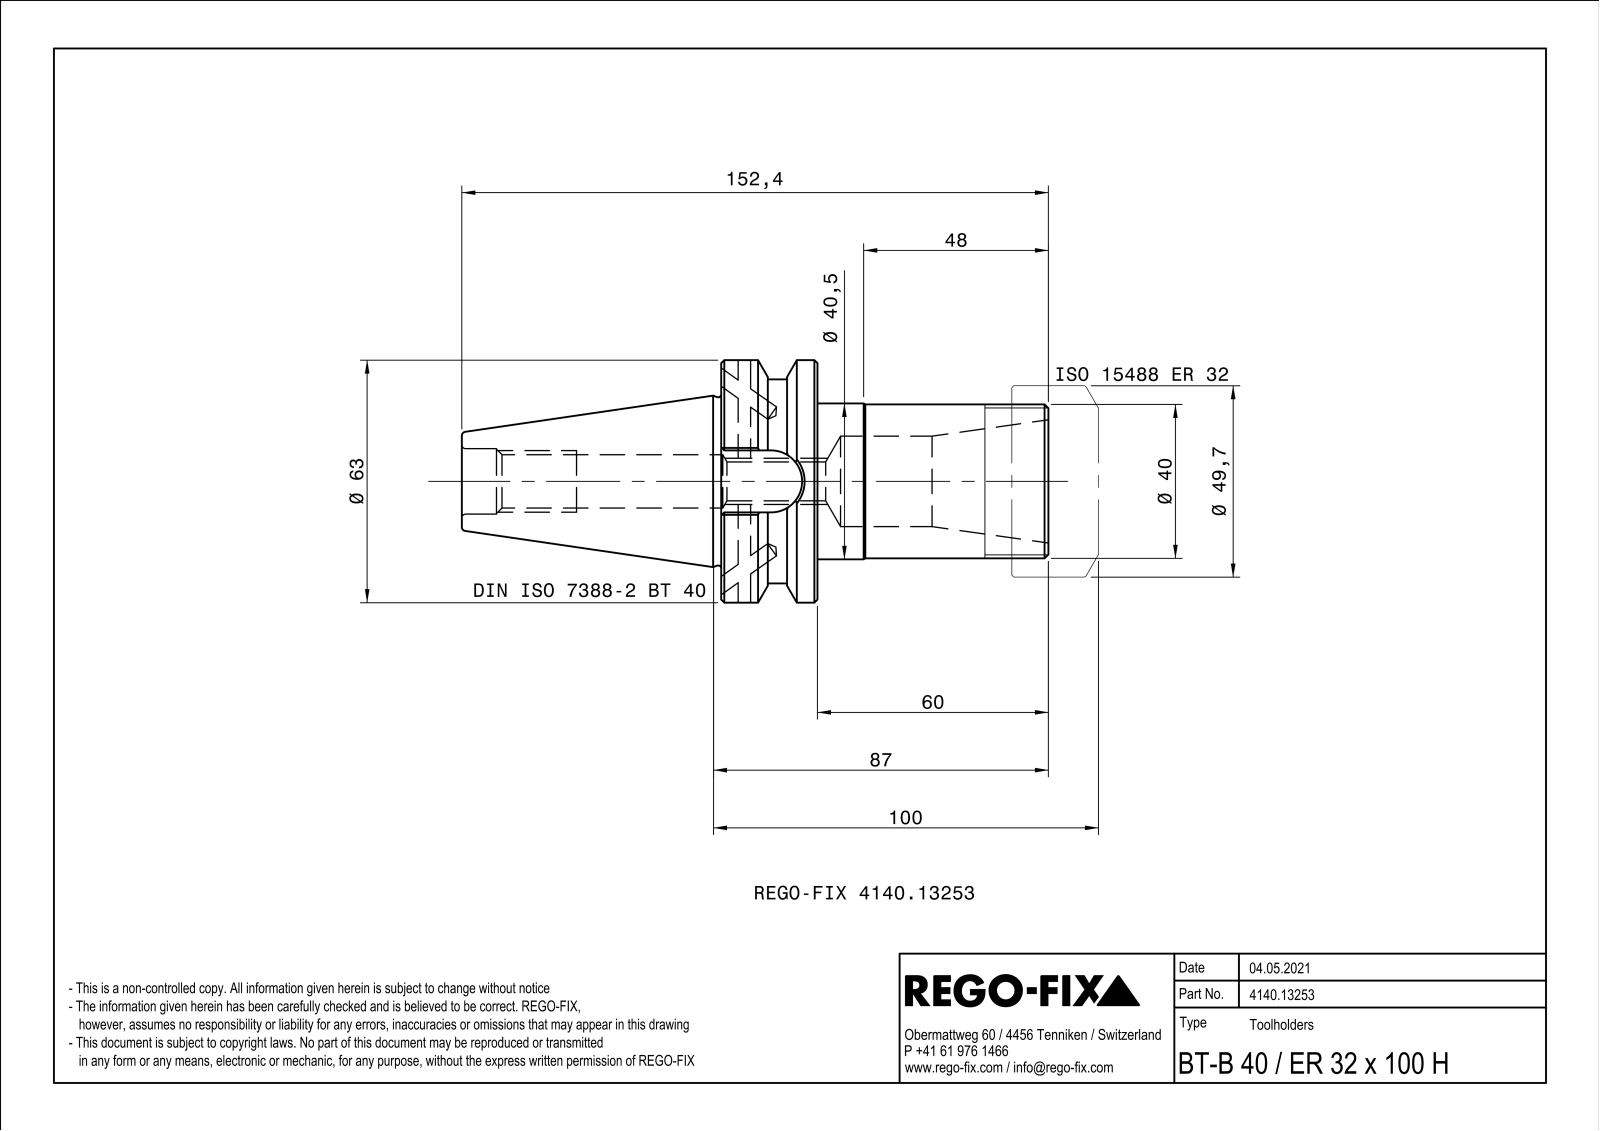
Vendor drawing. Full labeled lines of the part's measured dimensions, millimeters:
Part name (STEP PRODUCT): NOCUT
STEP written by: SIEMENS PLM Software Solid Edge ST10 (AUTOMOTIVE_DESIGN)
Units: millimetres
Bodies: 1 solid, 104 faces (36 planar, 29 cylindrical, 39 other)
Overall size (bounding box): 152.4 × 63 × 63
Volume: 166 506 mm³ · Surface area: 34 576 mm²
Round holes (diameter × count): ⌀3.24 ×2, ⌀3.9 ×2, ⌀10.11 ×1, ⌀13.83 ×1, ⌀13.84 ×1, ⌀17 ×1, ⌀23.5 ×1
Round bosses / shafts (diameter × count): ⌀63 ×1, ⌀53 ×1, ⌀40.5 ×1, ⌀40 ×1
Partial cylindrical surfaces — rounded edges, fillets, slot ends (radius × count): R0.5 ×4, R8.05 ×1
Main face-to-face distances: 25, 60, 85, 45.1, 152.4, 92.4, 67.4, 16.1, 67.9, 7.9
